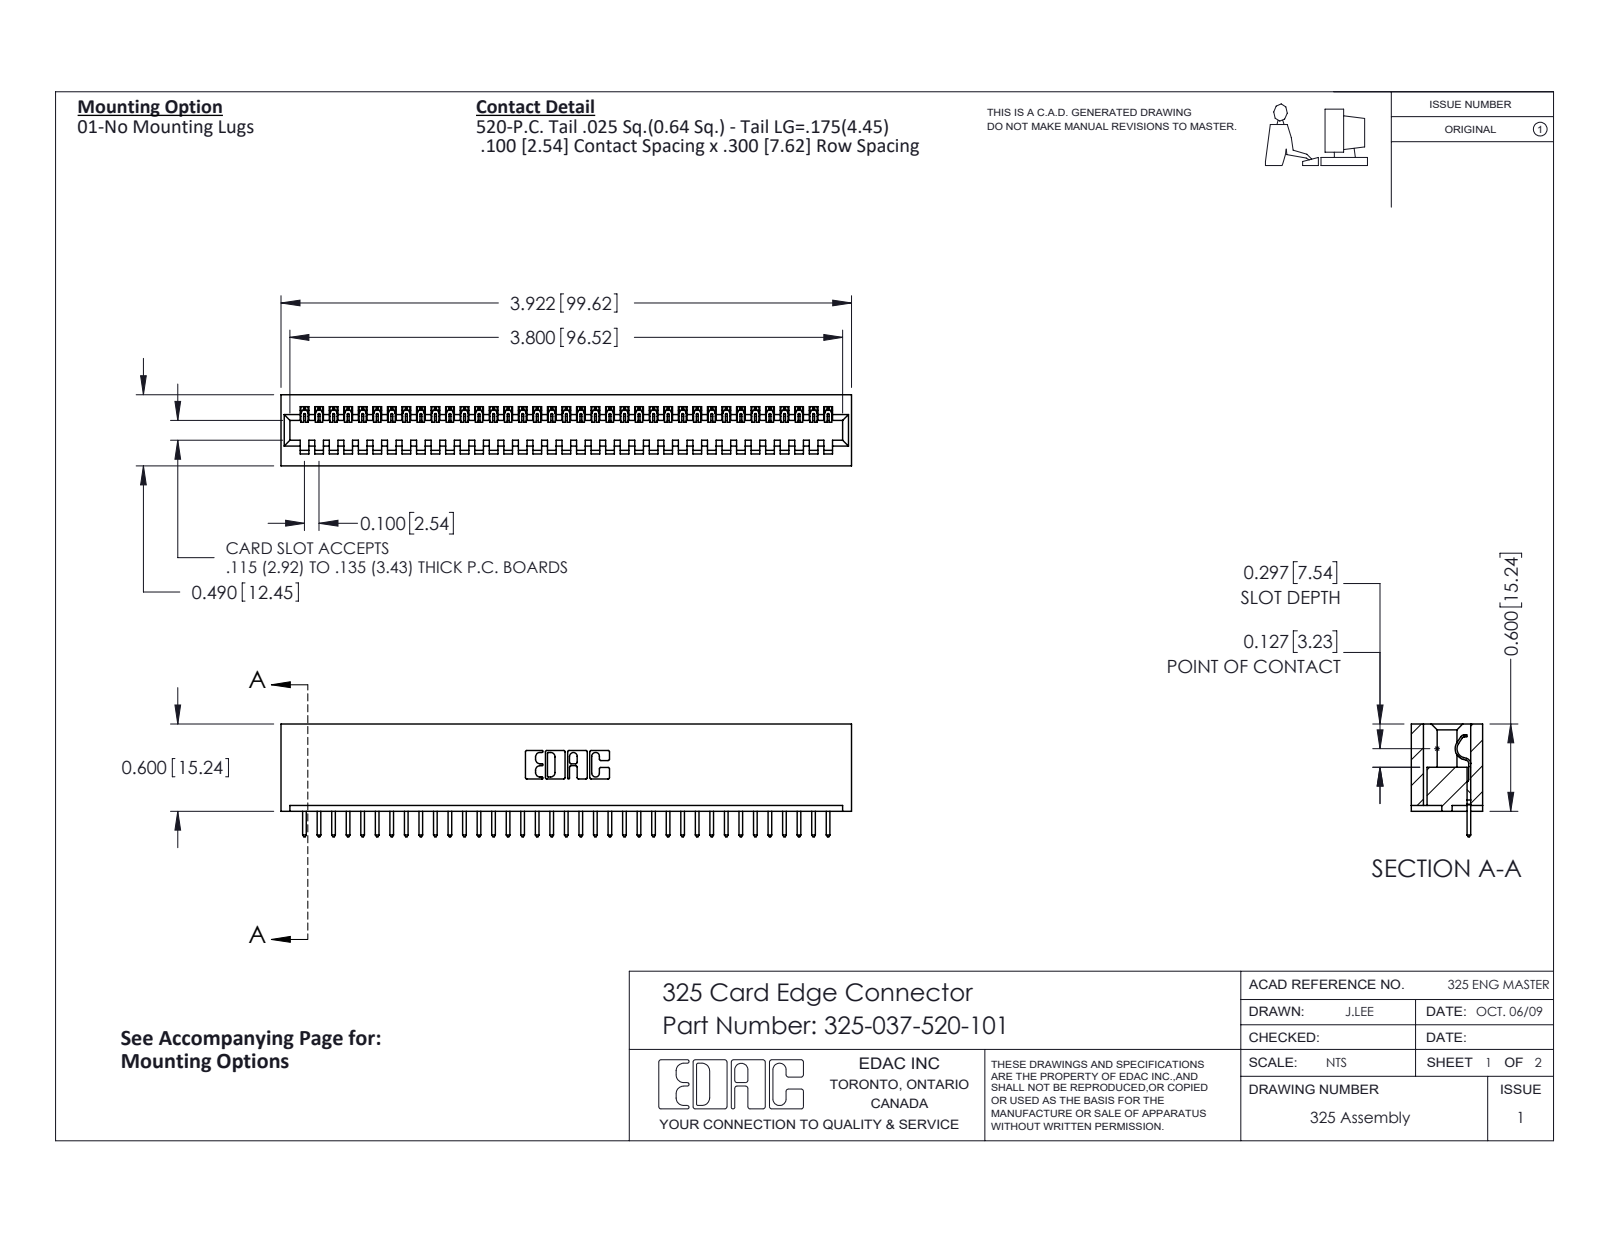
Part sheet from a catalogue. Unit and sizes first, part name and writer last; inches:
Units: inches
Overall size (bounding box): 3.922 × 0.775 × 0.49
Partial cylindrical surfaces — rounded edges, fillets, slot ends (radius × count): R0.006 ×74, R0.01 ×74, R0.01 ×22, R0.007 ×6, R0.031 ×6, R0.026 ×3, R0.014 ×1, R0.022 ×1
Main face-to-face distances: 0.083, 0.407, 0.49, 0.3, 0.107, 0.383, 0.025, 0.325, 0.56, 0.263
Volume: 0.798 in³ · Surface area: 22.18 in²
Bodies: 38 solids, 2252 faces (1620 planar, 632 cylindrical, 0 other)
Part name (STEP PRODUCT): 325 Part_Lugless; 325-037-520-101; 325-292-001_325-293-120
STEP written by: SolidWorks 2016 (CONFIG_CONTROL_DESIGN)
